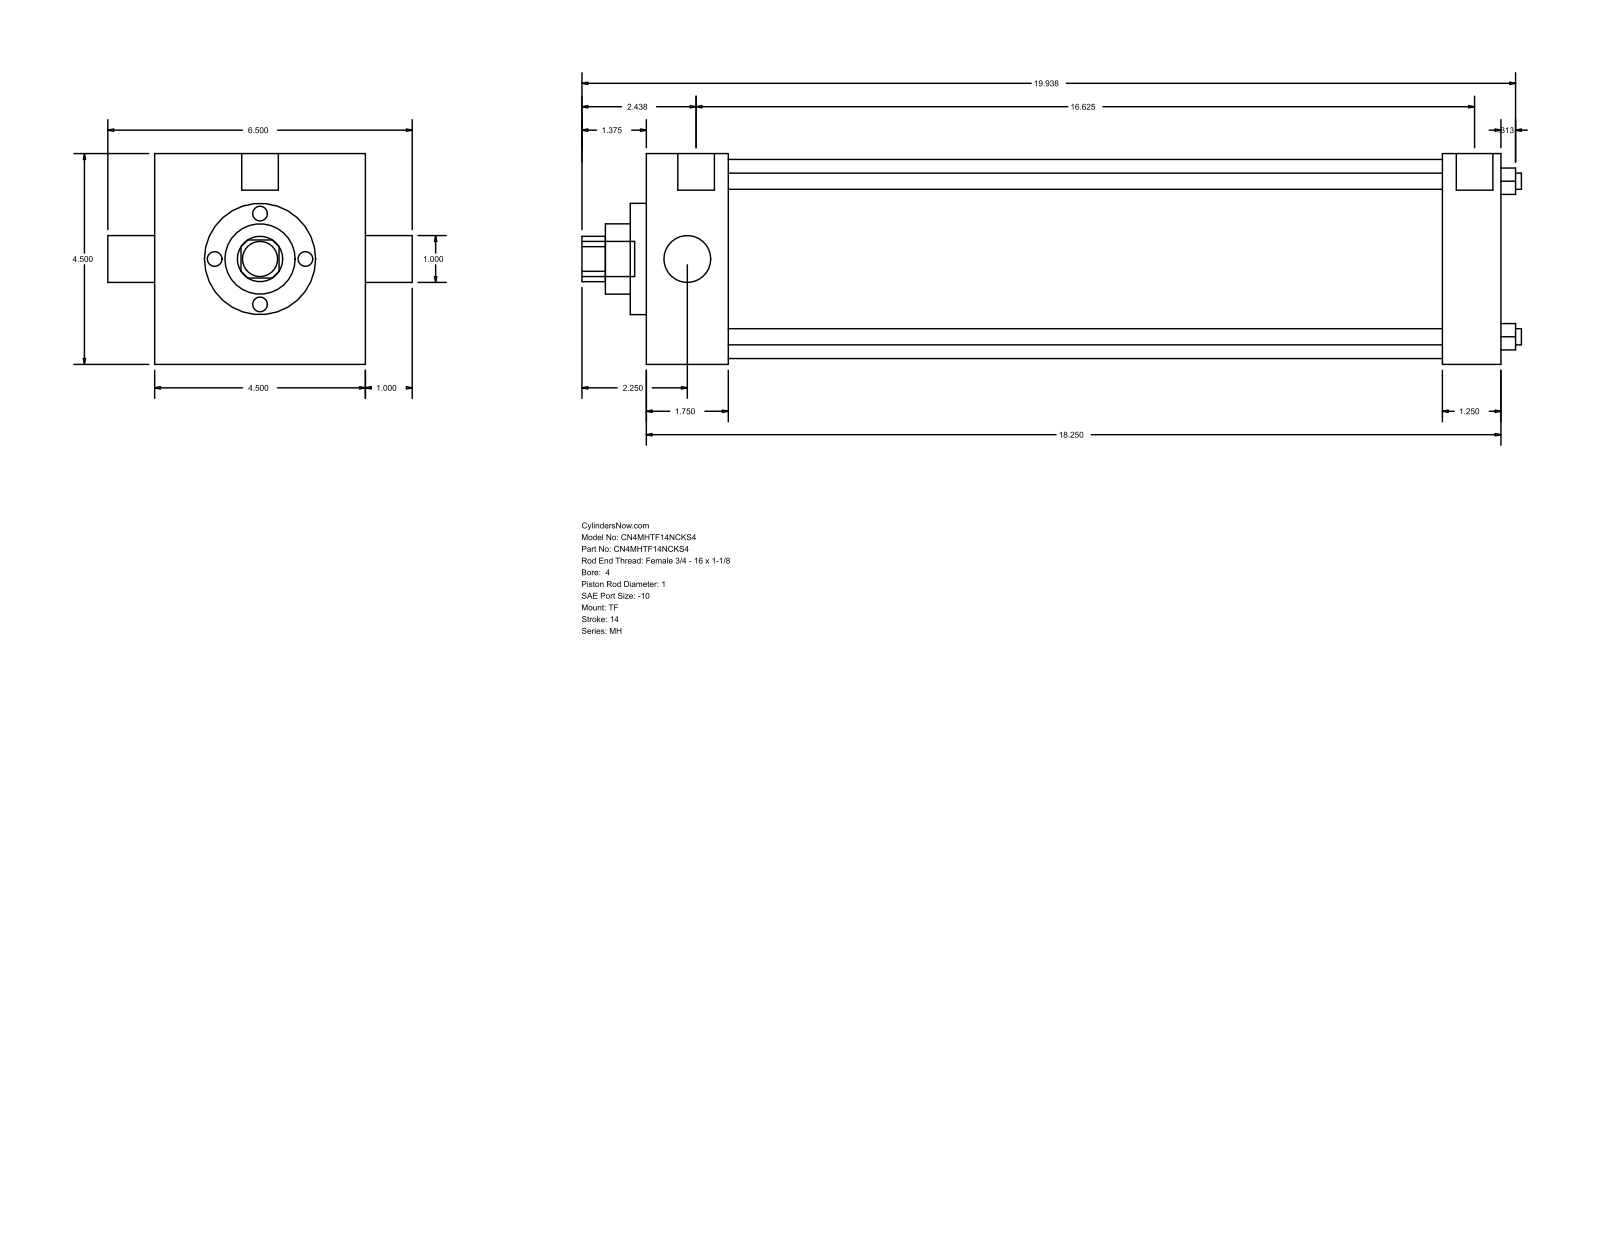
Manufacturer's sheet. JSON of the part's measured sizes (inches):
{"part_name": "MH_TF__0400_1", "step_written_by": "GSSL Pune (CONFIG_CONTROL_DESIGN)", "units": "inches", "bodies": {"solids": 0, "faces": 86, "planar": 61, "cylindrical": 25, "other": 0}, "overall_size": [20.063, 6.5, 4.5], "round_holes": [[0.345, 4], [1, 2], [1.5, 1], [2.375, 1], [4.25, 1]], "round_bosses_or_shafts": [[0.344, 3], [0.781, 2], [0.75, 1]], "partial_cylinders_radius": [[0.484, 1]], "face_to_face_distances": [4.5, 18.25, 1.75, 16.5, 17, 15.25, 1.25, 0.344, 2.094, 17.344], "hole_center_spacings": [2.347, 3.32, 4.695]}
